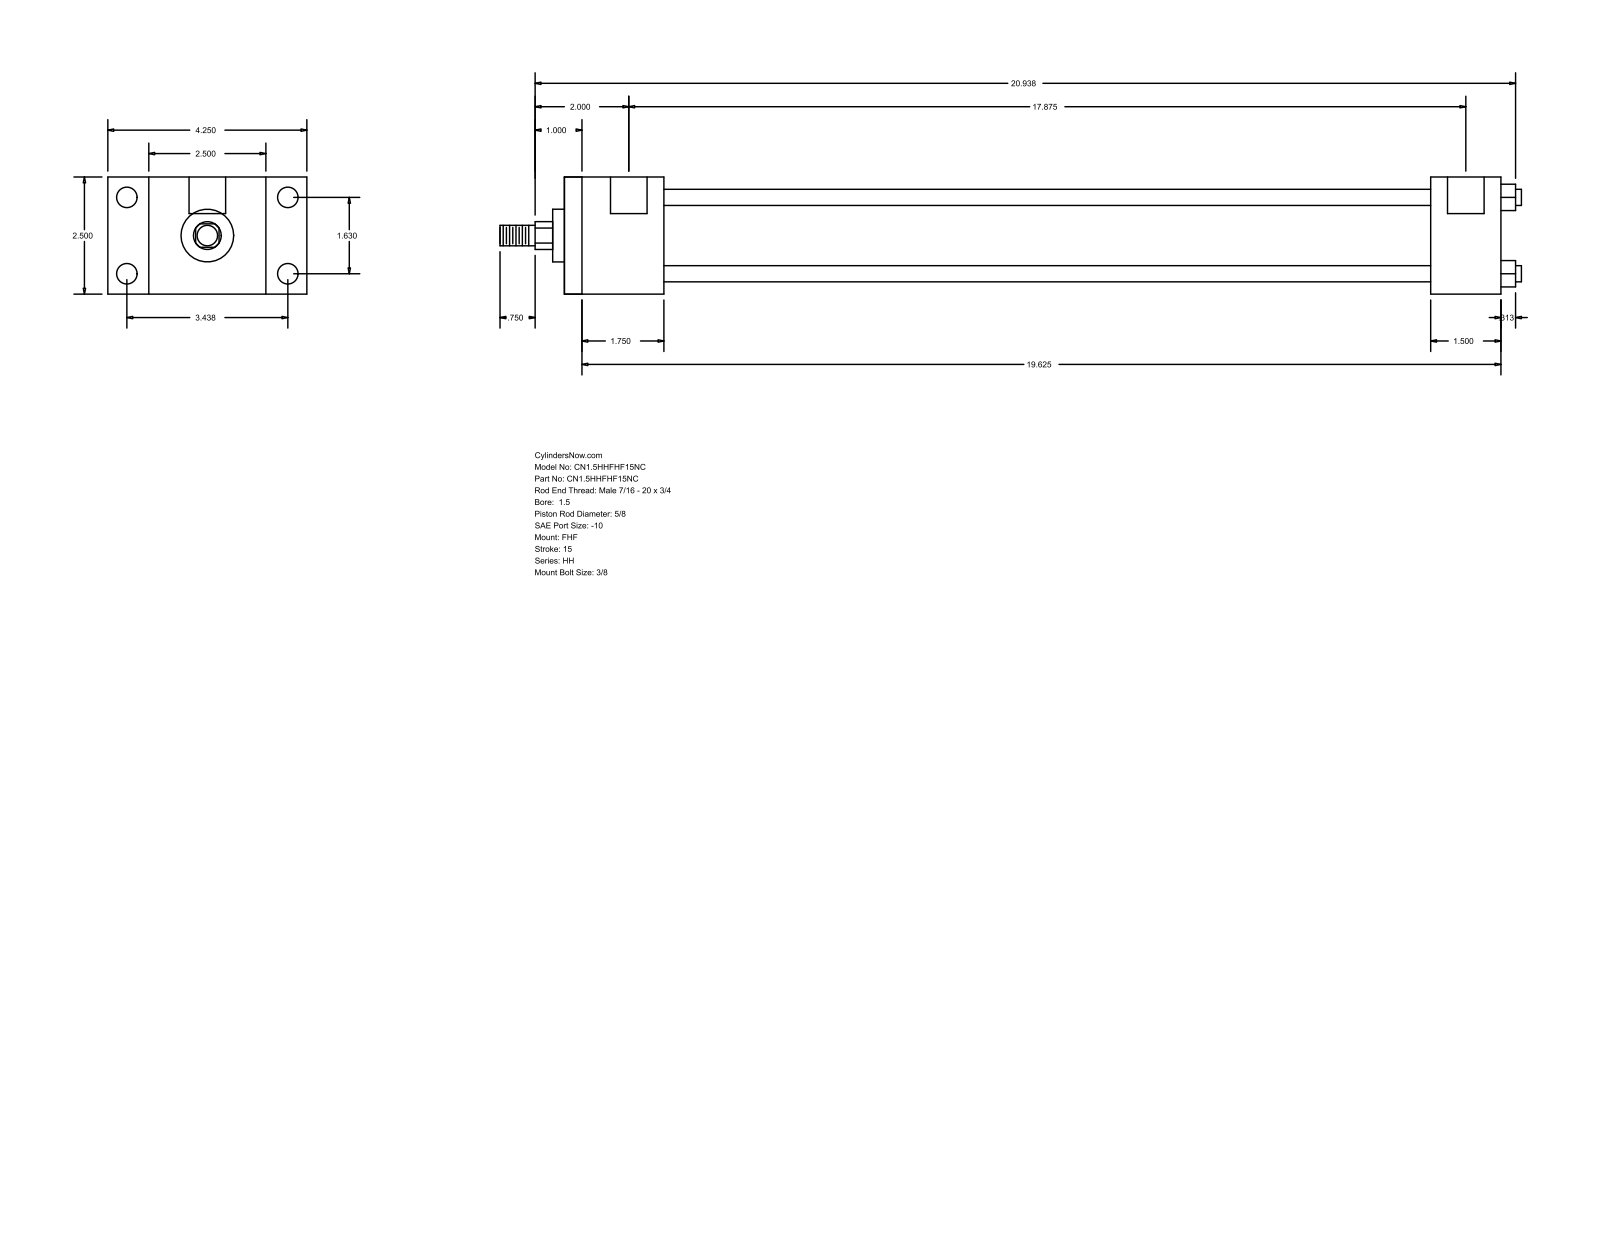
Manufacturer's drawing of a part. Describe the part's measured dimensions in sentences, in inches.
The part is named "HH_FHF__0150_0.625". Its 3-D file was written by "GSSL Pune (CONFIG_CONTROL_DESIGN)". It is 0 solids with 88 faces: 60 planar, 28 cylindrical and 0 other. Overall it measures 21.813 by 4.25 by 2.5 inches. Round holes: 4 of diameter 0.219, 4 of diameter 0.438, 2 of diameter 0.781. Round bosses or shafts: 4 of diameter 0.345, 1 of diameter 1.75, 1 of diameter 1.125, 1 of diameter 0.625, 1 of diameter 0.437. Partial cylindrical surfaces (rounded edges, fillets, slot ends): 1 of radius 0.297. The main face-to-face distances are 2.5, 0.875, 3.375, 2.125, 4.25, 20, 17.875, 18.5, 16.375, 1.5. The hole center spacings are 0.063, 1.63, 3.438, 3.805, 17.937, 18, 17.875.
